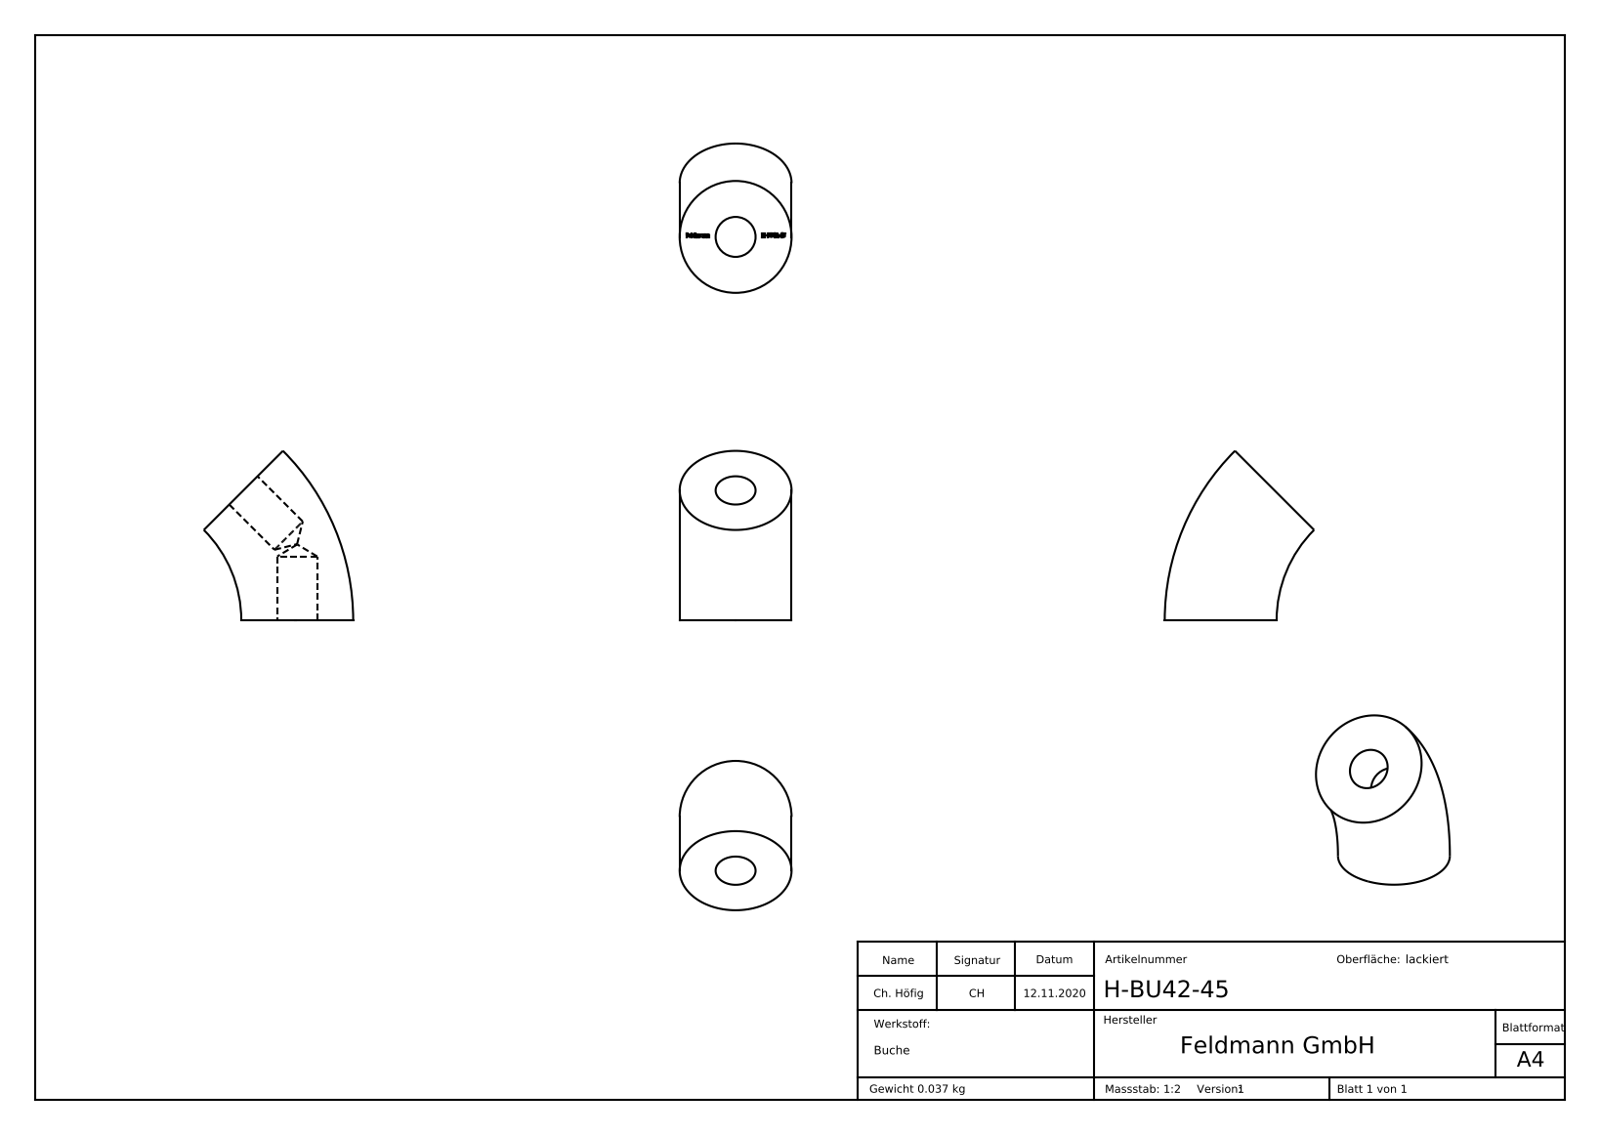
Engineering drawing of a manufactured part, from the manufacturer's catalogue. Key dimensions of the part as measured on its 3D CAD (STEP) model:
Part name (STEP PRODUCT): H-BU42-45
STEP written by: SolidWorks 2018 (CONFIG_CONTROL_DESIGN)
Units: millimetres
Bodies: 1 solid, 241 faces (153 planar, 4 cylindrical, 84 other)
Overall size (bounding box): 63.64 × 56.06 × 42
Volume: 66 067 mm³ · Surface area: 12 252 mm²
Round holes (diameter × count): ⌀15 ×2
Main face-to-face distances: 0.44, 0.88, 4.61, 2.97, 28.56, 0.79, 30.42, 1.86, 29.35, 26.54
